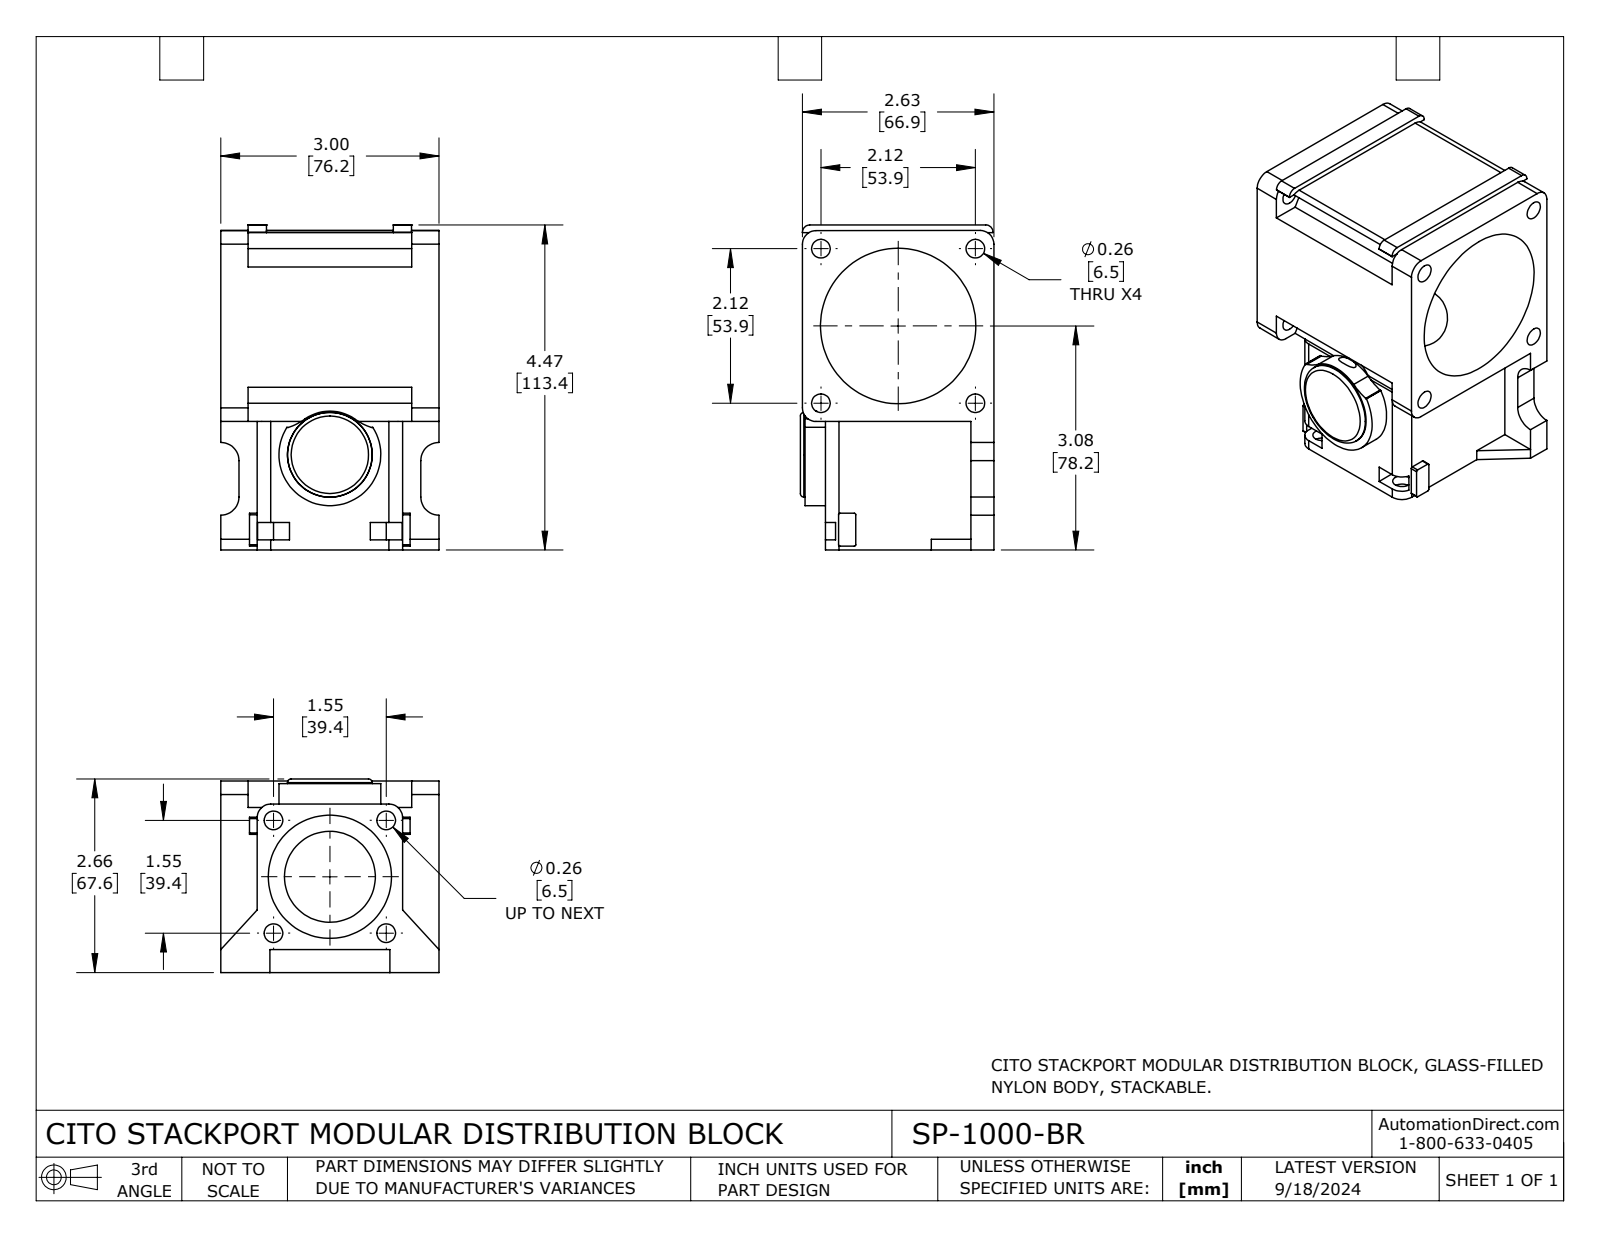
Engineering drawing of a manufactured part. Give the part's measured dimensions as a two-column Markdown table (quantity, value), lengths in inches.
| quantity | value |
| --- | --- |
| part name | SP-1000-BR |
| STEP written by | SolidWorks 2023 (CONFIG_CONTROL_DESIGN) |
| units | inches |
| bodies | 2 solids, 190 faces (109 planar, 73 cylindrical, 8 other) |
| overall size | 4.468 × 3 × 2.661 |
| volume | 12.9 in³ |
| surface area | 100.8 in² |
| round holes (diameter × count) | 0.256 × 4, 0.257 × 4, 0.52 × 1, 1.08 × 1, 1.25 × 1, 1.693 × 1, 2.136 × 1 |
| partial cylindrical surfaces (radius × count) | 0.02 × 6, 0.25 × 4, 0.187 × 3, 0.1 × 2, 0.819 × 2, 0.187 × 1, 0.188 × 1, 0.6 × 1 |
| main face-to-face distances | 2.5, 0.5, 2.632, 0.316, 2.316, 2, 3, 0.471, 2.124, 1.766 |
| hole center spacings | 1.502, 2.124, 1.096, 1.096, 1.55, 1.55, 2.192, 3.003 |
